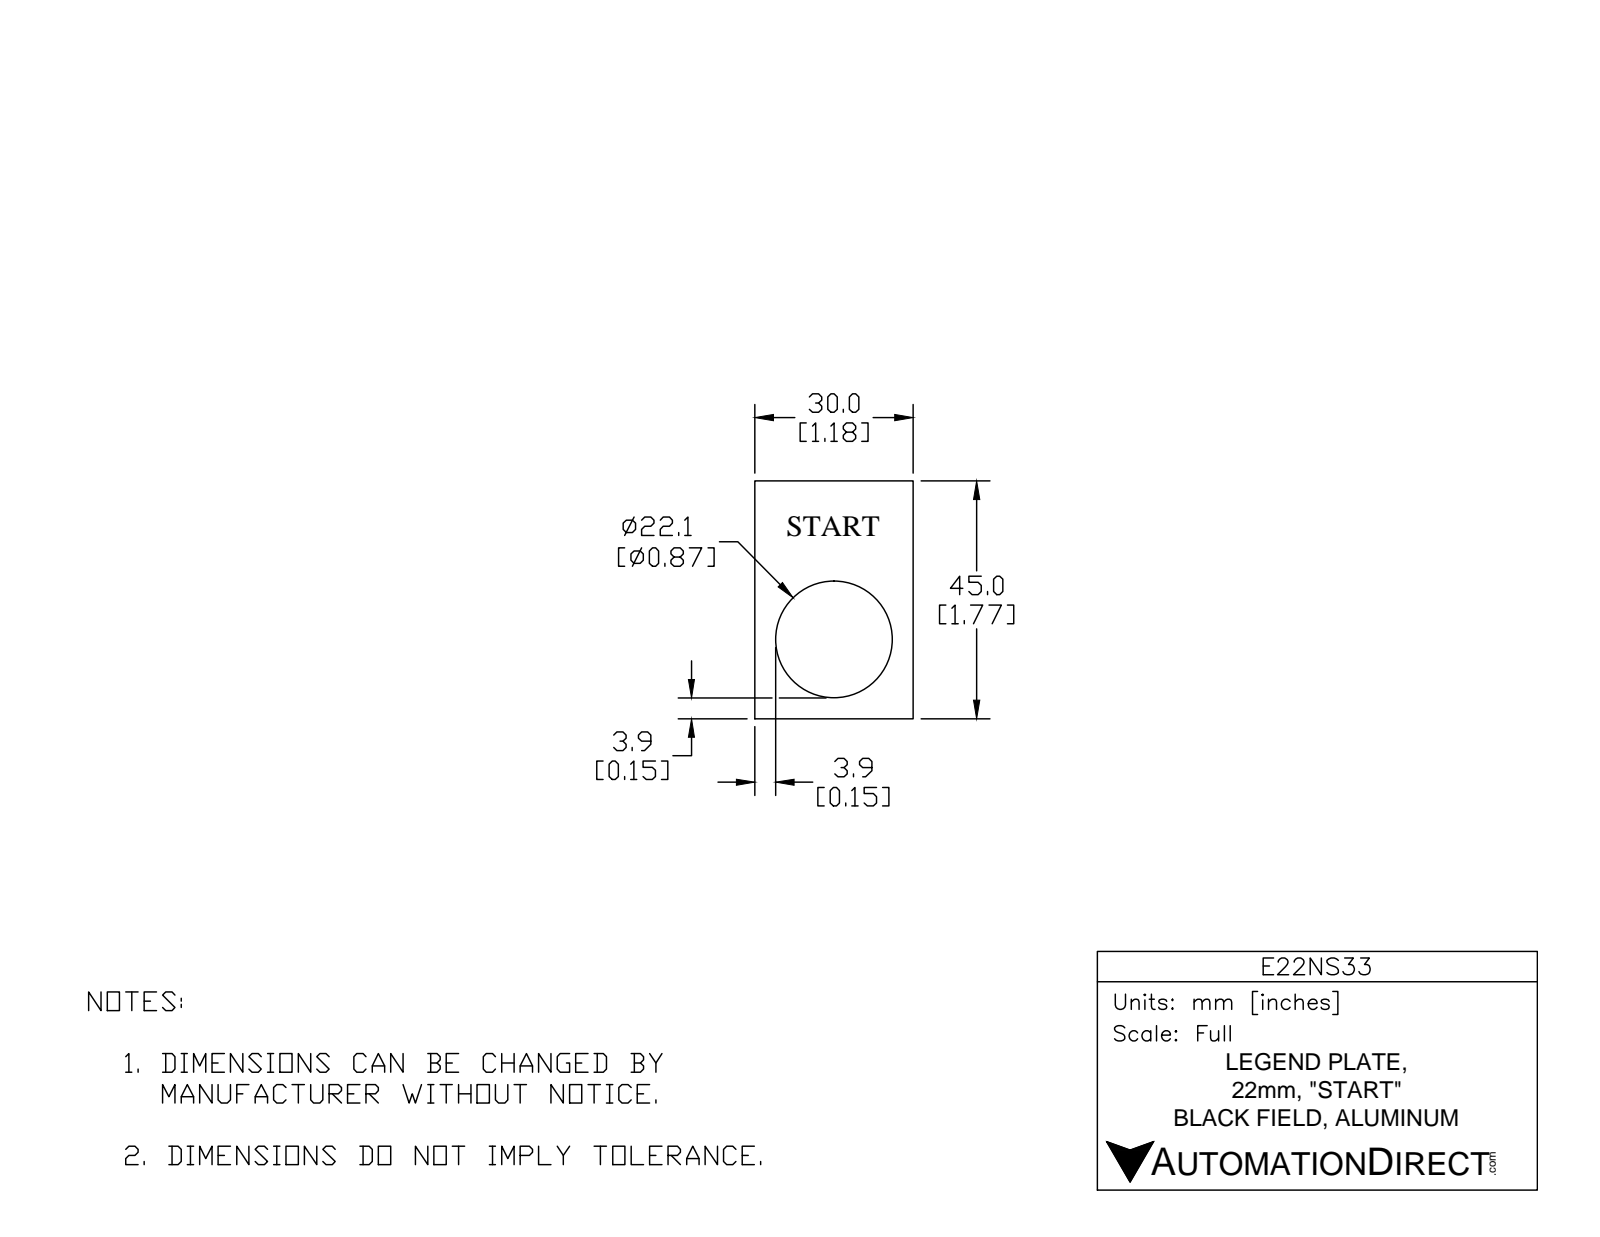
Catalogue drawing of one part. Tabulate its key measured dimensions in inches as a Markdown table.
| quantity | value |
| --- | --- |
| part name | E22NS33 |
| STEP written by | SolidWorks 2017 (AUTOMOTIVE_DESIGN) |
| units | inches |
| bodies | 1 solid, 79 faces (56 planar, 3 cylindrical, 20 other) |
| overall size | 1.772 × 1.181 × 0.051 |
| volume | 0.076 in³ |
| surface area | 3.47 in² |
| round holes (diameter × count) | 0.874 × 1 |
| main face-to-face distances | 0.051, 1.181, 1.772, 0.041, 0.185, 1.587, 0.014, 0.387, 0.252, 0.528 |
